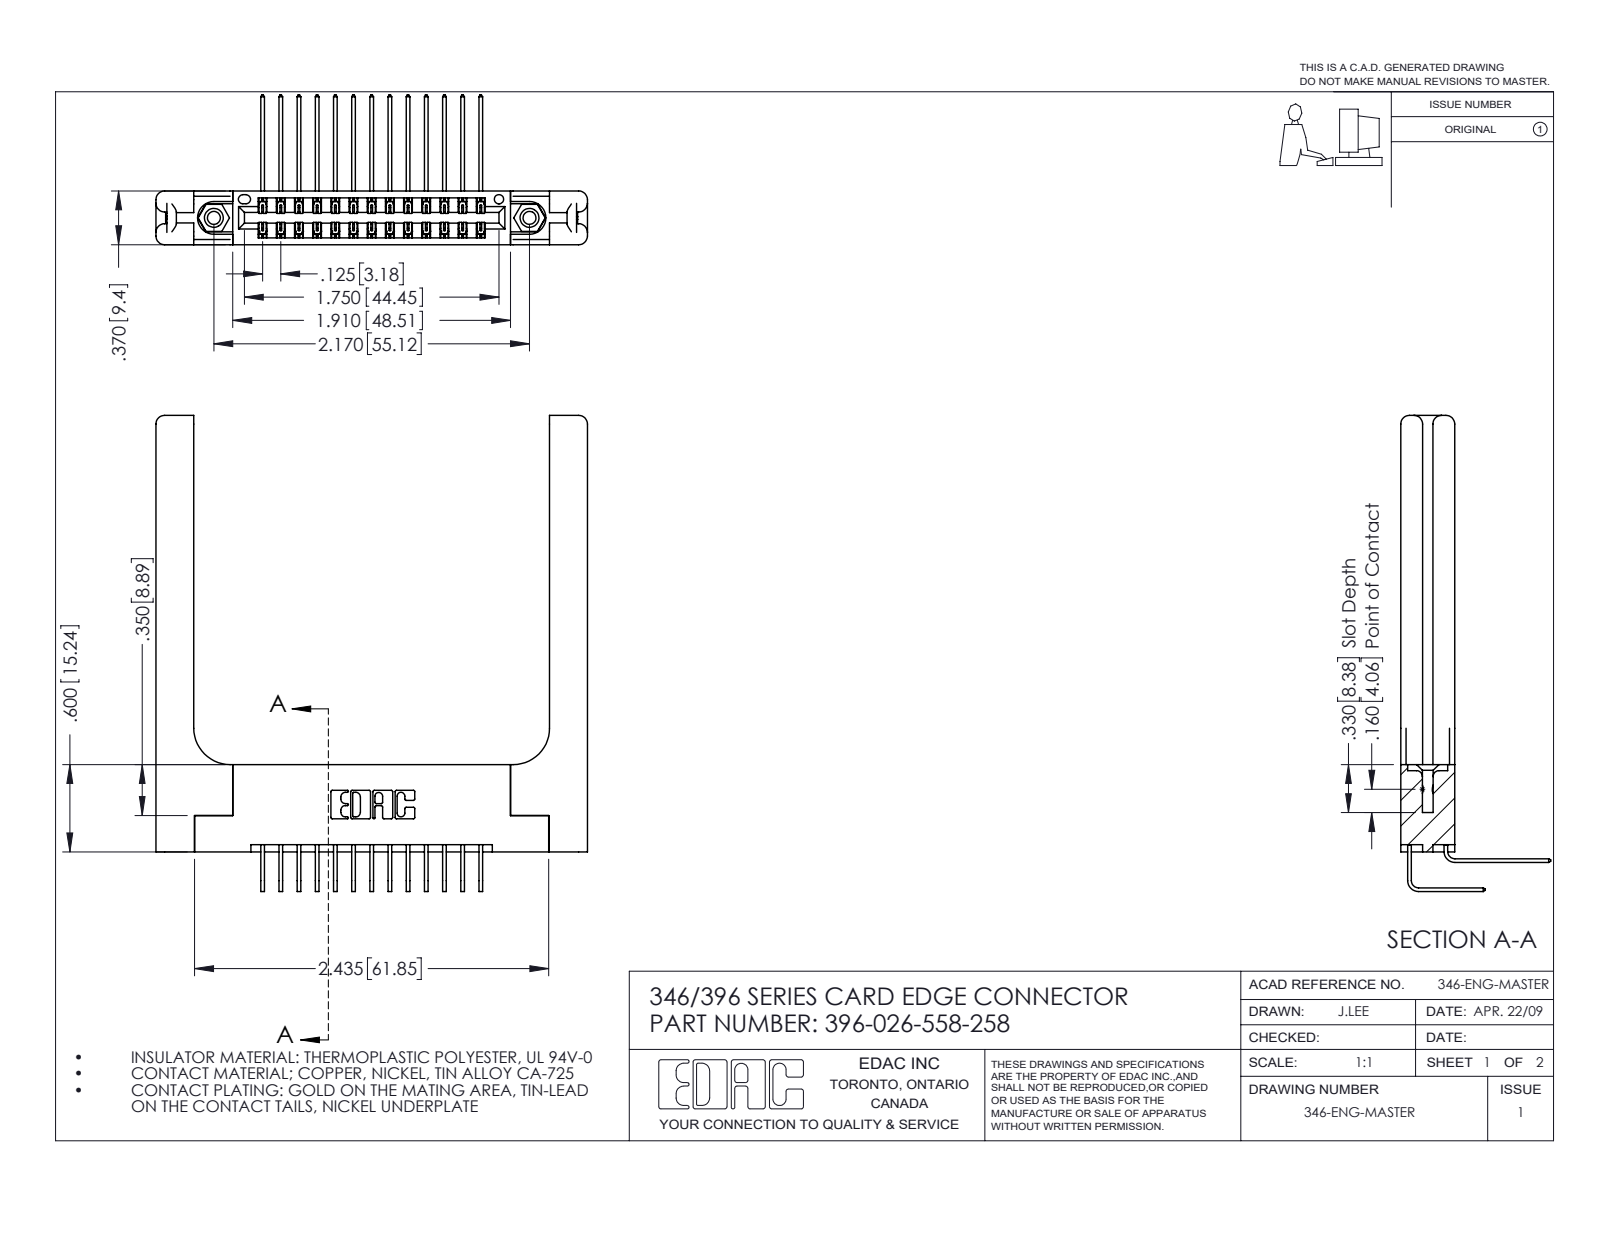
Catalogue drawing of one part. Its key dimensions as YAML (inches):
part_name: "345-292-001_558 Tail - 2; 345-292-001_558 559 Tail - 1; 346-220-058_345-220-058; 345-250-001_345-250-001-102 (+2 more)"
step_written_by: "SolidWorks 2016 (CONFIG_CONTROL_DESIGN)"
units: inches
bodies: {solids: 31, faces: 1782, planar: 1186, cylindrical: 536, other: 60}
overall_size: [3.273, 2.966, 1.03]
volume: 0.901
surface_area: 23.61
round_holes:
  - {diameter: 0.089, count: 2}
  - {diameter: 0.125, count: 2}
  - {diameter: 0.156, count: 2}
  - {diameter: 0.064, count: 1}
round_bosses_or_shafts:
  - {diameter: 0.155, count: 2}
partial_cylinders:
  - {radius: 0.006, count: 39}
  - {radius: 0.01, count: 22}
  - {radius: 0.06, count: 16}
  - {radius: 0.007, count: 6}
  - {radius: 0.031, count: 6}
  - {radius: 0.026, count: 3}
  - {radius: 0.014, count: 2}
  - {radius: 0.022, count: 2}
face_to_face_distances: [0.37, 0.072, 0.15, 0.322, 0.048, 0.148, 0.025, 0.25, 0.298, 0.102]
hole_center_spacings: [0.246, 1.964, 2.17]
